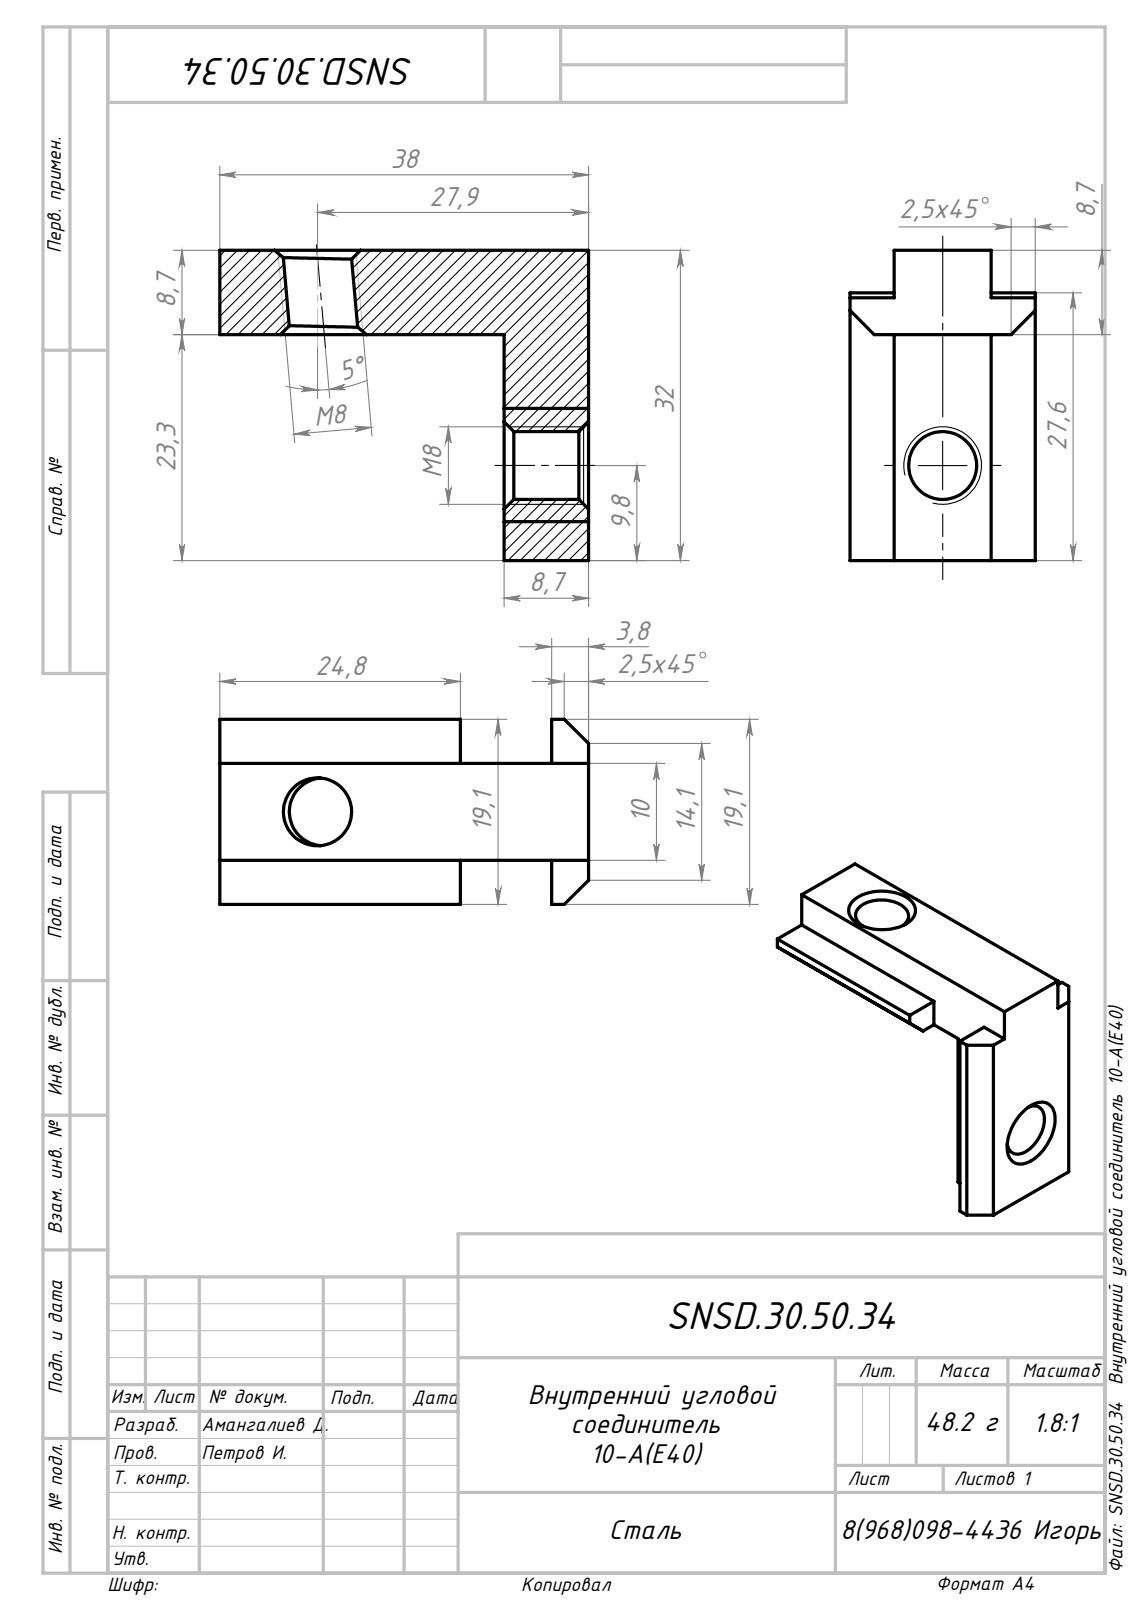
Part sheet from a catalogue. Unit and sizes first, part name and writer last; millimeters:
Units: millimetres
Overall size (bounding box): 38 × 32 × 19.1
Round holes (diameter × count): ⌀7 ×2
Main face-to-face distances: 8.7, 3.8, 4.9, 10, 4.55, 14.55, 32, 27.1, 23.3, 38
Volume: 6 104 mm³ · Surface area: 3 565 mm²
Bodies: 1 solid, 36 faces (24 planar, 4 cylindrical, 8 other)
STEP written by: SolidWorks 2018 (AUTOMOTIVE_DESIGN)
